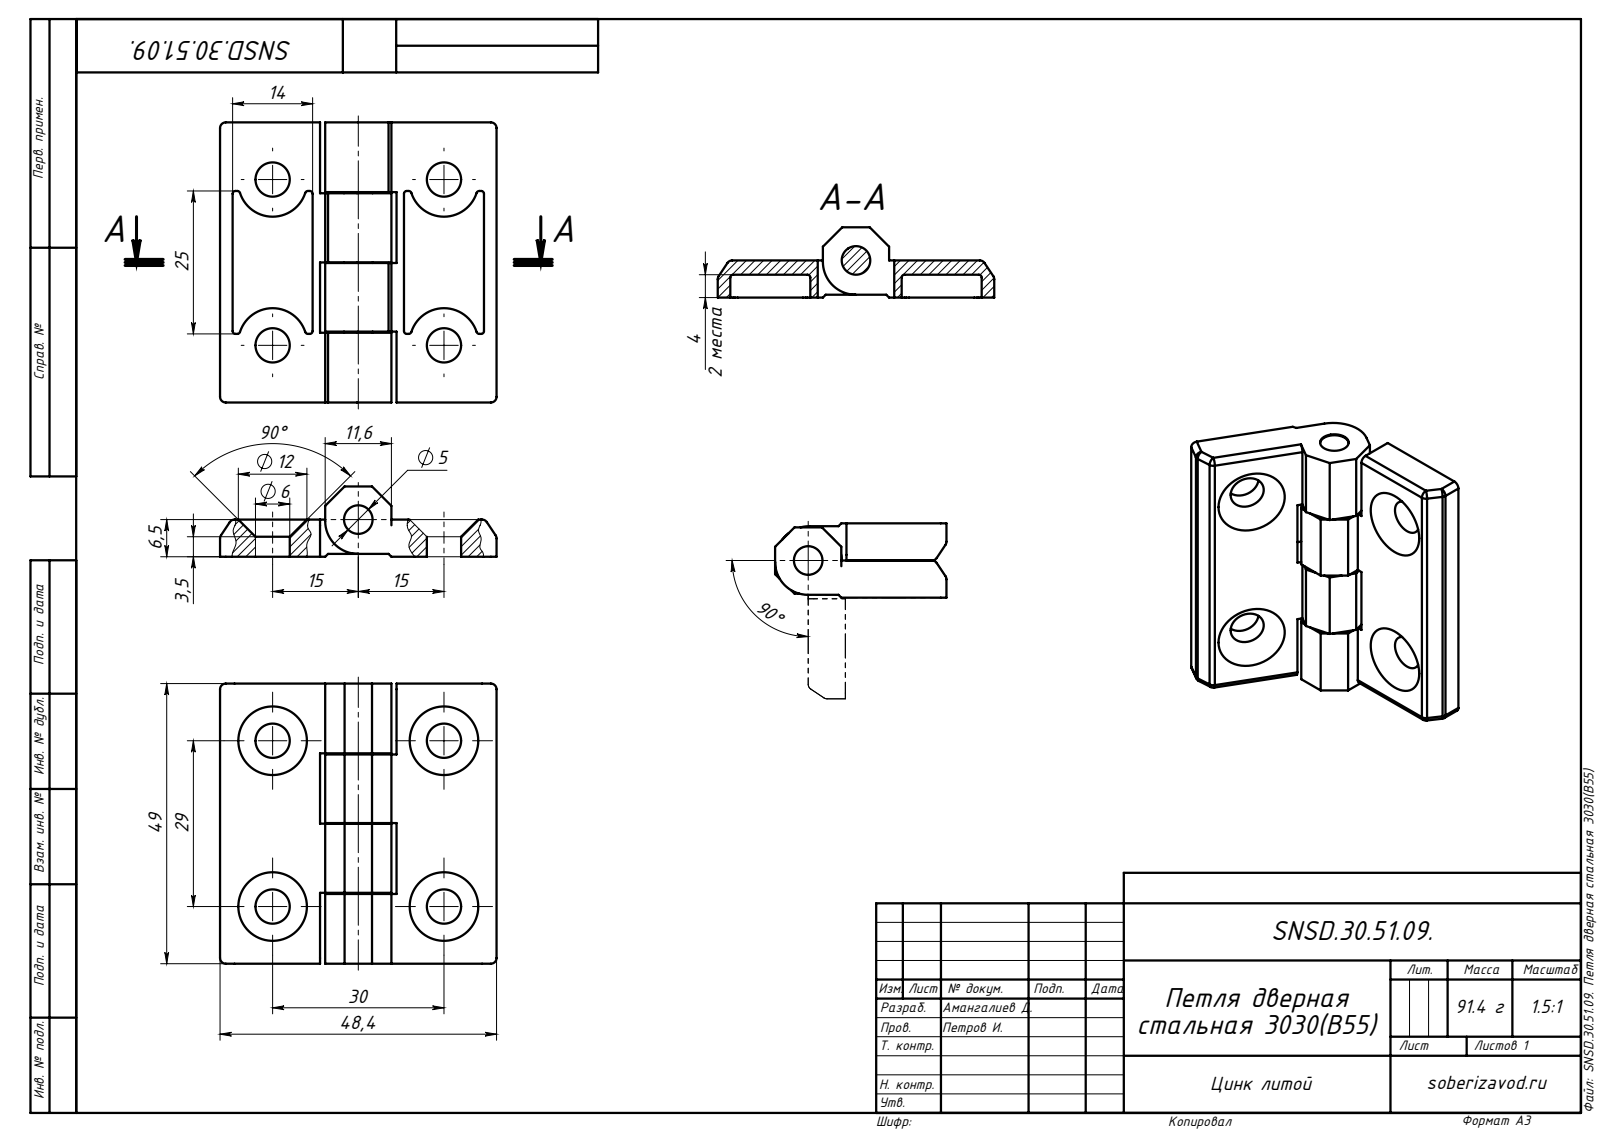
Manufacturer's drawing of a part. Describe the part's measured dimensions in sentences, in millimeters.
The part is named "SNSD.30.51.09. Петля дверная стальная 3030(B55); SNSD.30.50.96. Петля дверная алюминевая 3045(B47)E07B48B54B55_00". Its 3-D file was written by "SolidWorks 2014 (AUTOMOTIVE_DESIGN)". It is 3 solids with 172 faces: 66 planar, 70 cylindrical and 36 other. Overall it measures 49 by 48.39 by 12.29 millimeters. Its volume is 13 476 cubic millimeters and its surface area 9 623 square millimeters. Round holes: 4 of diameter 6, 1 of diameter 5. Partial cylindrical surfaces (rounded edges, fillets, slot ends): 22 of radius 0.5, 14 of radius 1, 5 of radius 6, 1 of radius 5.74. The main face-to-face distances are 6.5, 4, 2.5, 12.2, 29.99, 2.2, 16.2, 24.4, 12.4, 17.5. The hole center spacings are 29, 29.99, 41.72.
